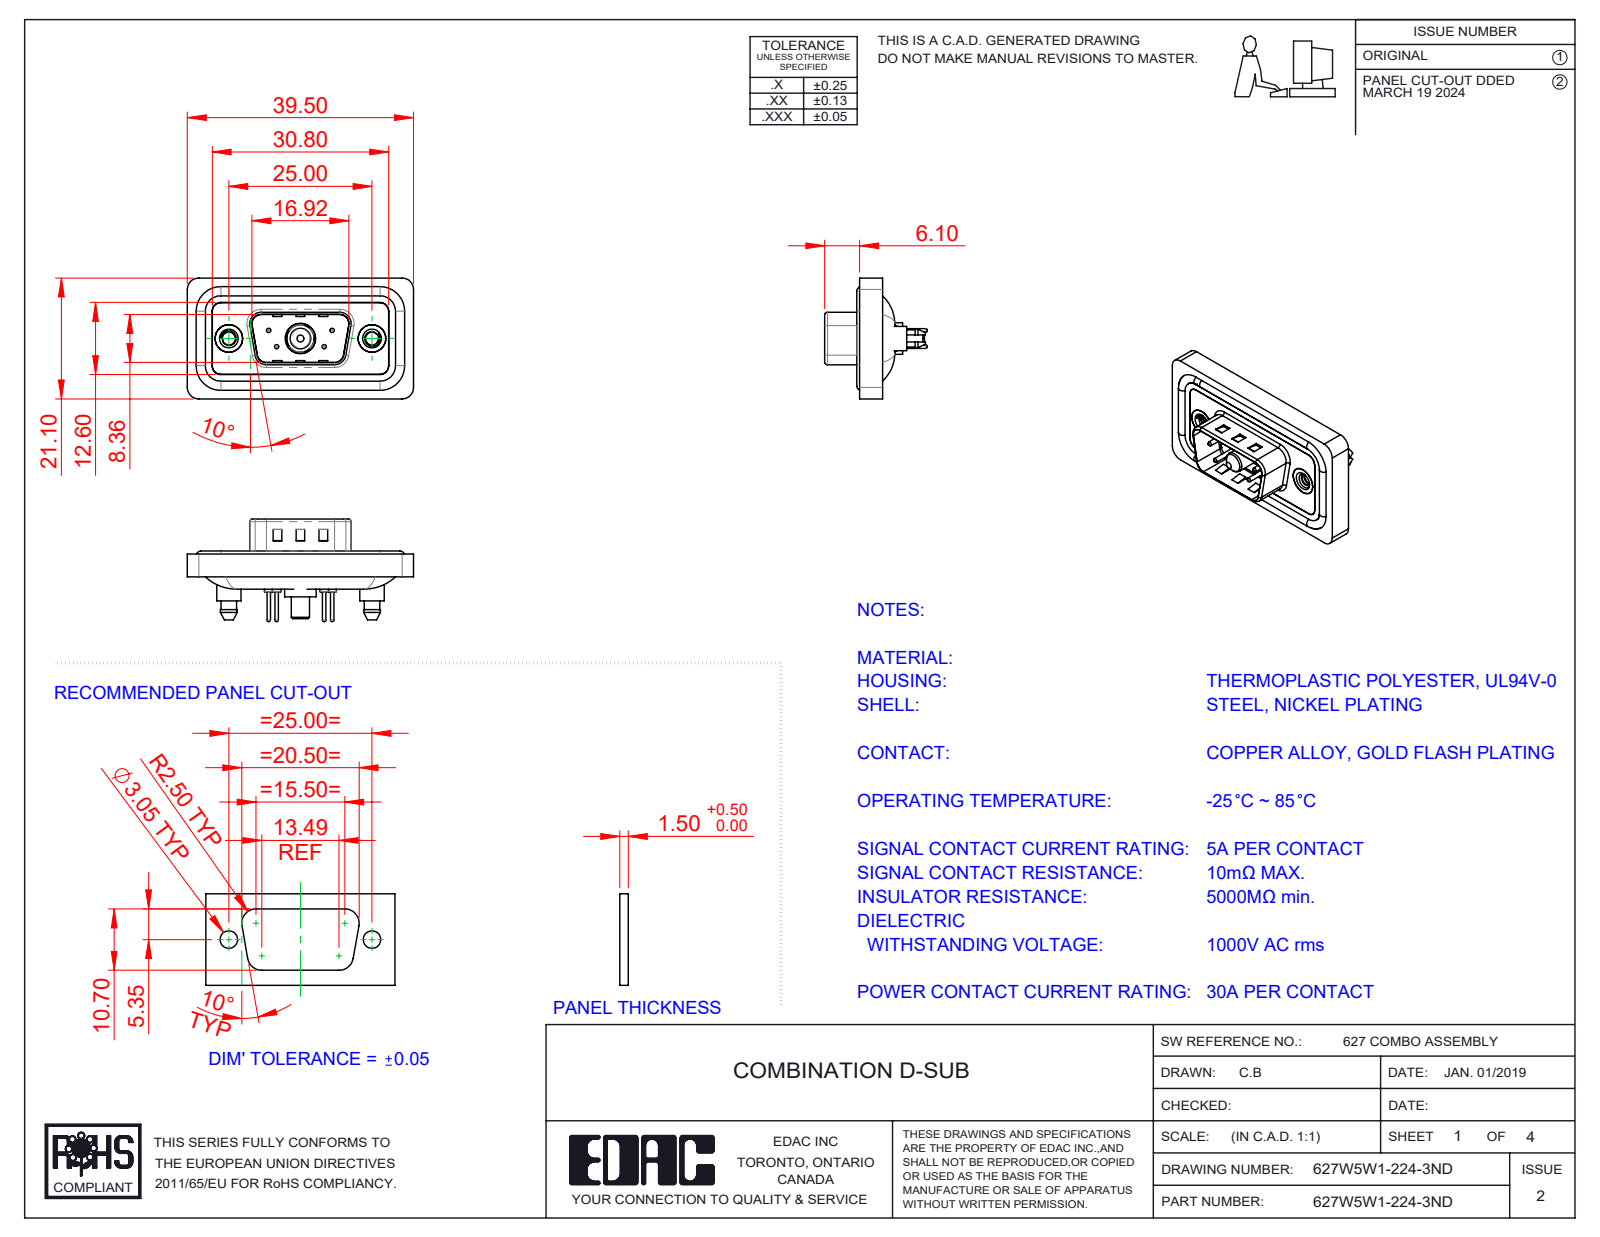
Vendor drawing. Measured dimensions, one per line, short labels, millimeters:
name: 627Combo Threaded Boardlock_5; Power Pin_30A S; 627Combo Housing_5W1; 627Combo Contact Row 1_24 (+6 more)
written by: SolidWorks 2023 (CONFIG_CONTROL_DESIGN)
unit: mm
bodies: 13 solids, 656 faces (199 planar, 295 cylindrical, 162 other)
size: 39.5 × 21.1 × 17.9
volume: 4 529 mm³; area: 7 282 mm²
holes: 4× ⌀0.75, 4× ⌀1.6, 4× ⌀2, 2× ⌀2.26, 2× ⌀4, 2× ⌀4.8, 2× ⌀5, 1× ⌀4.85, 1× ⌀5.3
bosses: 4× ⌀1.6, 4× ⌀1.5, 4× ⌀0.6, 2× ⌀5.4, 2× ⌀4.9, 2× ⌀4.25, 1× ⌀5.5, 1× ⌀5.2
rounds: 24× R1.5, 18× R2, 10× R1.6, 8× R0.5, 4× R0.25, 4× R0.6, 4× R0.65, 4× R0.9
face distances: 0.4, 1.1, 2.9, 1.6, 1.5, 3.1, 0.5, 2.5, 4, 0.8
hole spacings: 3.16, 5.72, 7.1, 12.5, 18.1, 4.39, 4.4, 8.31
